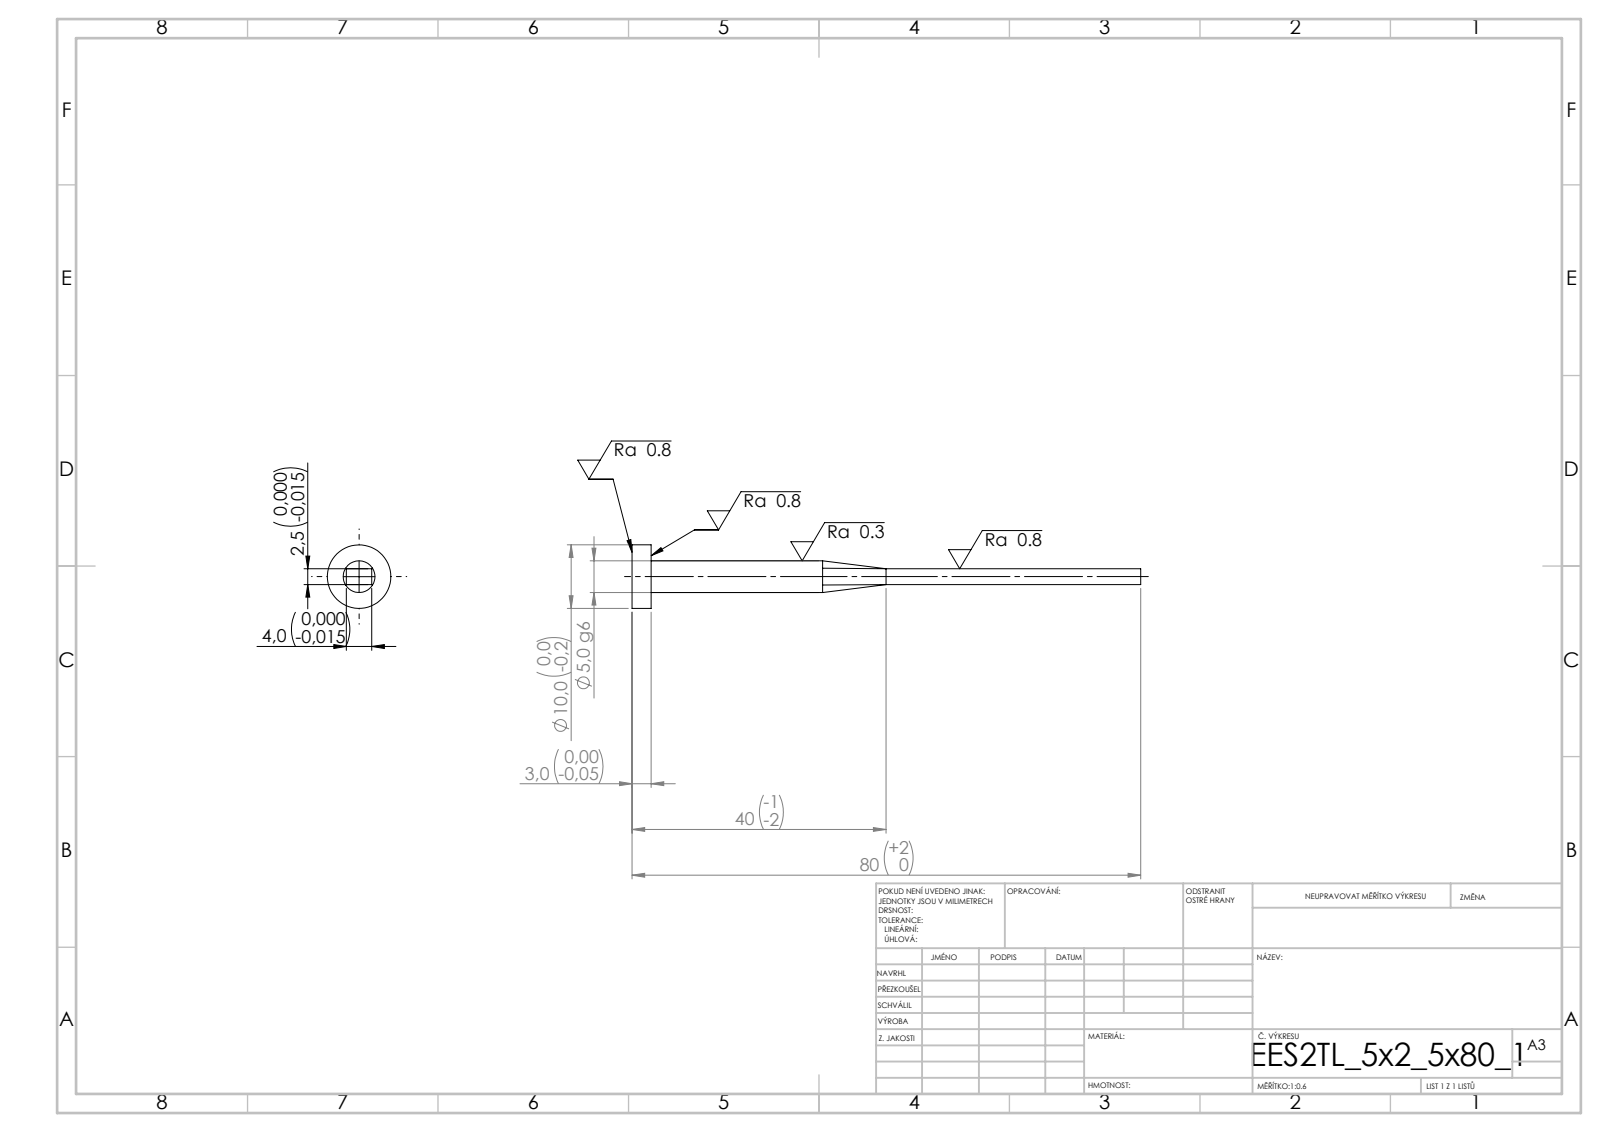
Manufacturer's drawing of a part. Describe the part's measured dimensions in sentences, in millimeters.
Its 3-D file was written by "SolidWorks 2019 (CONFIG_CONTROL_DESIGN)". It is 1 solid with 15 faces: 7 planar, 4 cylindrical and 4 other. Overall it measures 80.1 by 10 by 10 millimeters. Its volume is 1 313 cubic millimeters and its surface area 1 328 square millimeters. Round bosses or shafts: 1 of diameter 10, 1 of diameter 5. The main face-to-face distances are 2.5, 4, 3, 80.1, 77.1.
